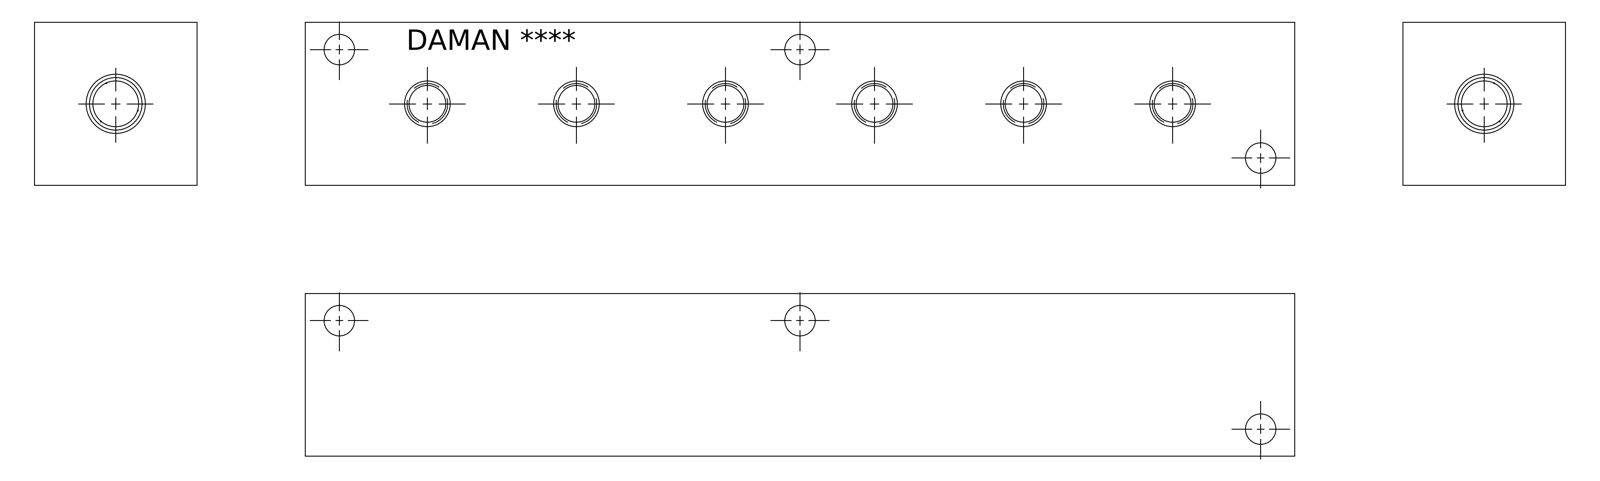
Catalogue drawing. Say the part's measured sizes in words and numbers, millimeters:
The part is named "Part_+H0000602P_3D". Its 3-D file was written by "Autodesk Inventor 2020 (AUTOMOTIVE_DESIGN)". It is 1 solid with 354 faces: 212 planar, 28 cylindrical and 114 other. Overall it measures 231.78 by 38.1 by 38.1 millimeters. Its volume is 320 023 cubic millimeters and its surface area 44 944 square millimeters. Round holes: 6 of diameter 7.14, 6 of diameter 8.43, 6 of diameter 10.33, 1 of diameter 10.72, 1 of diameter 13.87. The main face-to-face distances are 38.1, 231.78, 30.23, 7.87, 38.06, 7.83, 11.4, 220.37, 208.97, 220.38. The hole center spacings are 34.93, 69.85, 104.78, 34.92, 107.95, 110.9, 217.39, 21.58.
